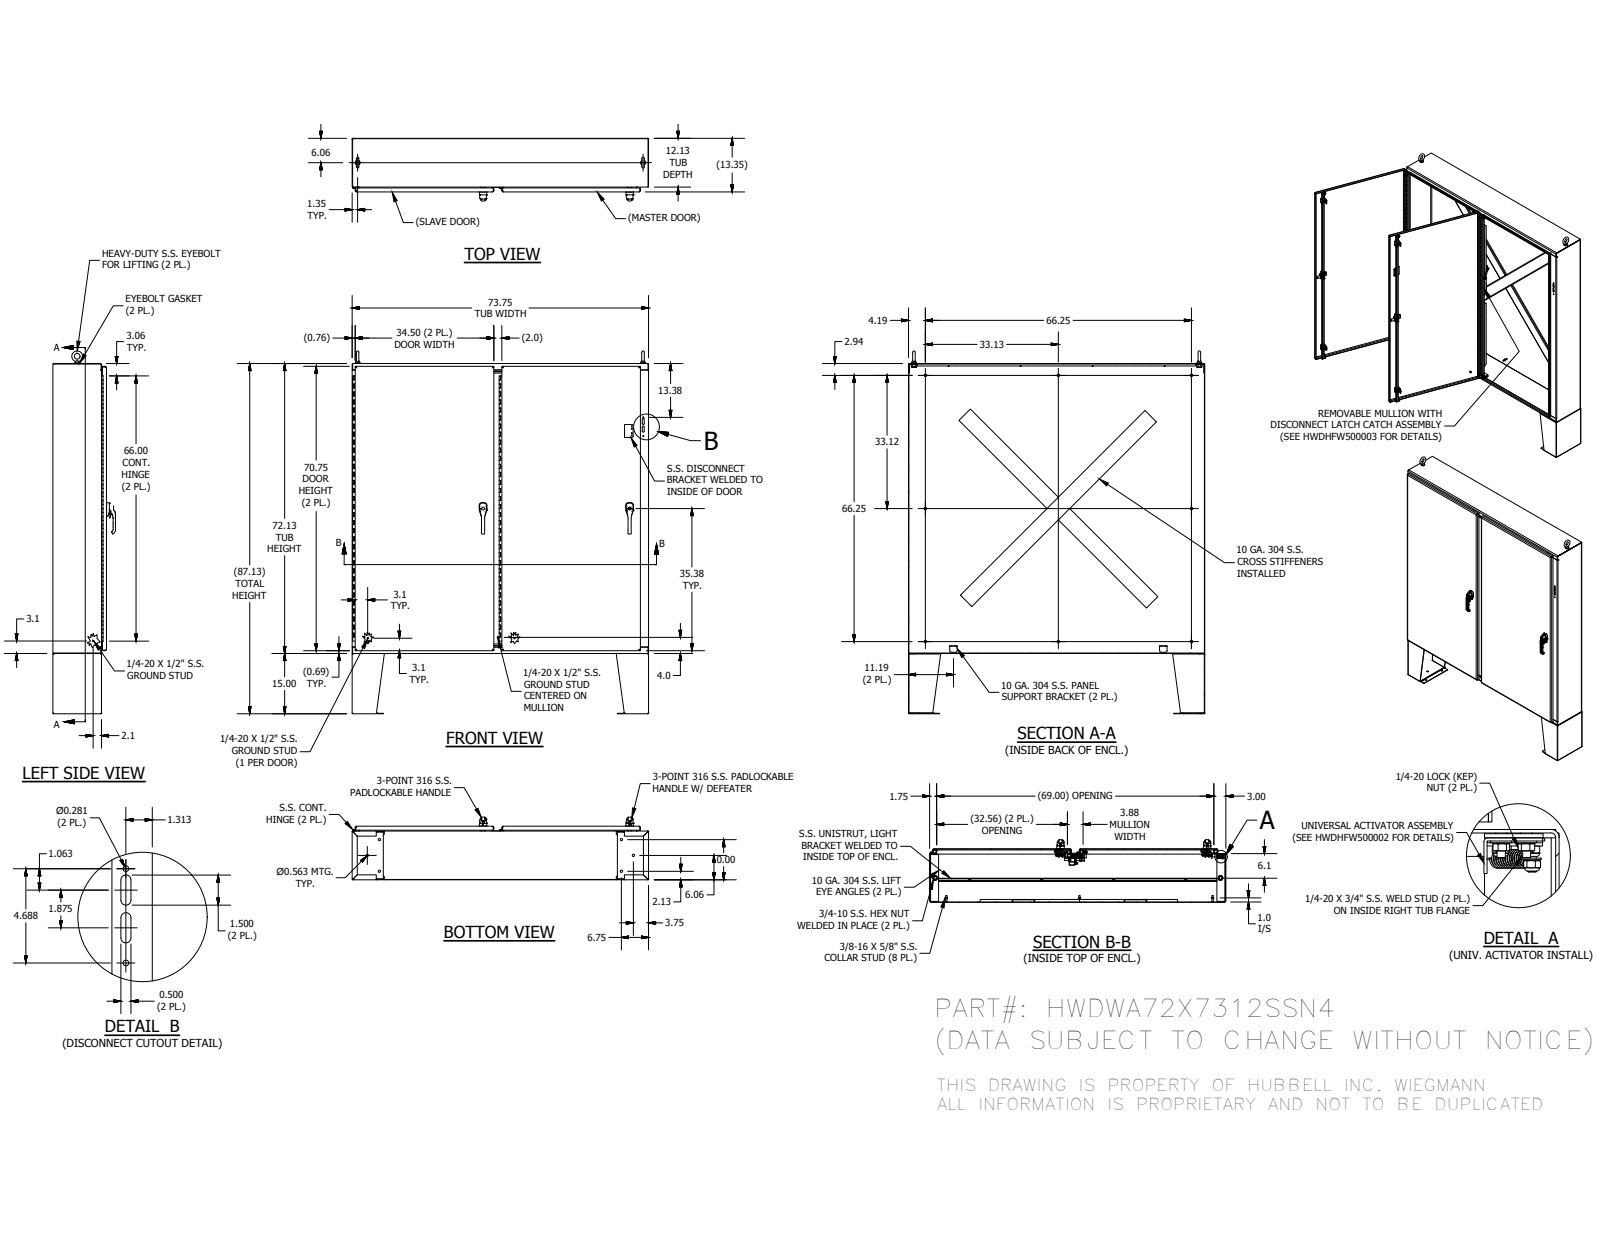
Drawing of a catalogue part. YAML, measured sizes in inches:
part_name: "WA72X7312SSN4BLR; WAX7312SSN4TOP; WAX7312SSN4BTM; HFW332010S (+8 more)"
step_written_by: "Autodesk Inventor 2016 (AUTOMOTIVE_DESIGN)"
units: inches
bodies: {solids: 220, faces: 9190, planar: 4286, cylindrical: 3104, other: 1800}
overall_size: [90.248, 73.75, 15.596]
volume: 1931
surface_area: 37260
round_holes:
  - {diameter: 0.375, count: 18}
  - {diameter: 0.563, count: 18}
  - {diameter: 0.25, count: 17}
  - {diameter: 0.196, count: 10}
  - {diameter: 0.187, count: 9}
  - {diameter: 0.19, count: 8}
  - {diameter: 0.262, count: 8}
  - {diameter: 0.281, count: 8}
  - {diameter: 0.289, count: 8}
  - {diameter: 0.335, count: 8}
  - {diameter: 0.38, count: 8}
  - {diameter: 0.156, count: 6}
round_bosses_or_shafts:
  - {diameter: 0.25, count: 21}
  - {diameter: 0.33, count: 18}
  - {diameter: 0.625, count: 13}
  - {diameter: 0.337, count: 12}
  - {diameter: 0.375, count: 11}
  - {diameter: 0.563, count: 9}
  - {diameter: 0.28, count: 8}
  - {diameter: 1, count: 6}
partial_cylinders:
  - {radius: 0.02, count: 359}
  - {radius: 0.012, count: 221}
  - {radius: 0.02, count: 192}
  - {radius: 0.125, count: 55}
  - {radius: 0.019, count: 42}
  - {radius: 0.05, count: 28}
  - {radius: 0.079, count: 28}
  - {radius: 0.25, count: 23}
face_to_face_distances: [0.104, 13.244, 13.14, 13.348, 72.021, 73.646, 12.021, 1.223, 11.917, 1.327]
hole_center_spacings: [0.38, 0.76, 1.195, 1.459, 3.503, 3.87, 4.89, 4.963]
